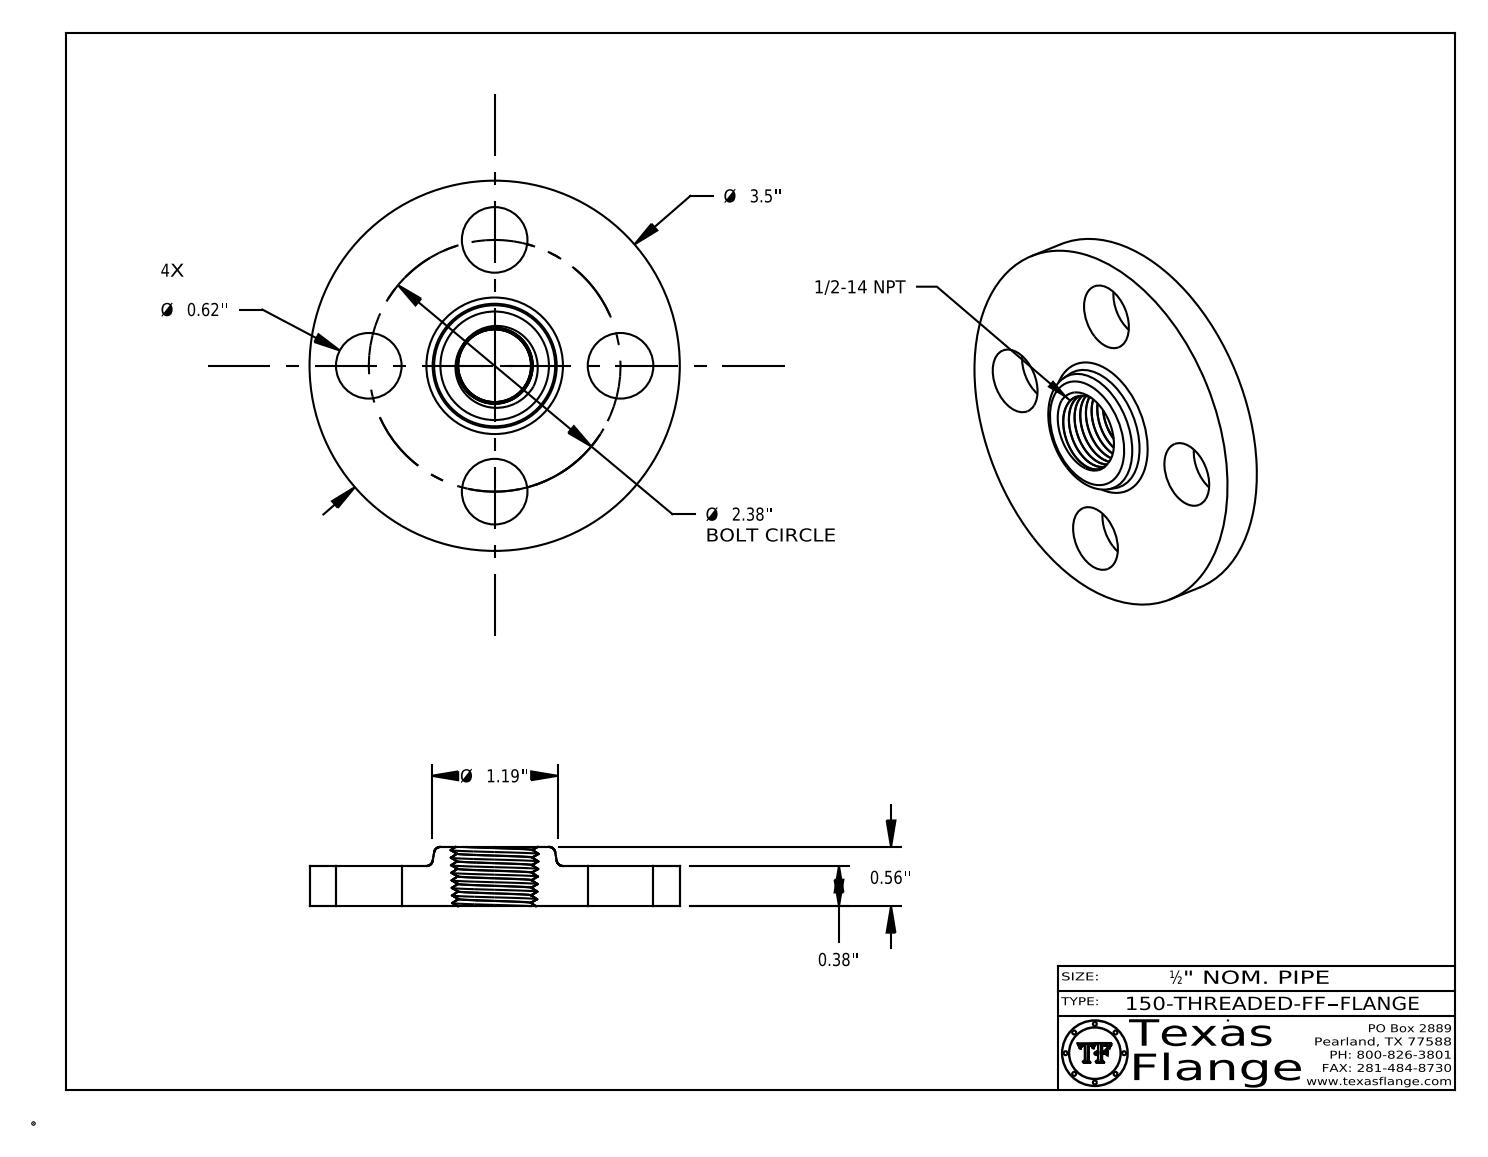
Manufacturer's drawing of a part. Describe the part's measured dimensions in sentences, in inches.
The part is named "150-THREADED-FF". Its 3-D file was written by "CATIA V5 STEP AP214 (AUTOMOTIVE_DESIGN)". It is 1 solid with 491 faces: 368 planar, 30 cylindrical and 93 other. Overall it measures 3.5 by 3.5 by 0.56 inches. Its volume is 3.133 cubic inches and its surface area 26.07 square inches. Round holes: 4 of diameter 0.62, 1 of diameter 0.495. Round bosses or shafts: 8 of diameter 0.03, 1 of diameter 3.5, 1 of diameter 0.39. The main face-to-face distances are 0.38, 0.56, 0.18, 0.365, 0.015, 0.195, 0.148, 0.145, 0.027, 0.122. The hole center spacings are 1.683, 0.911, 2.199, 2.38.
